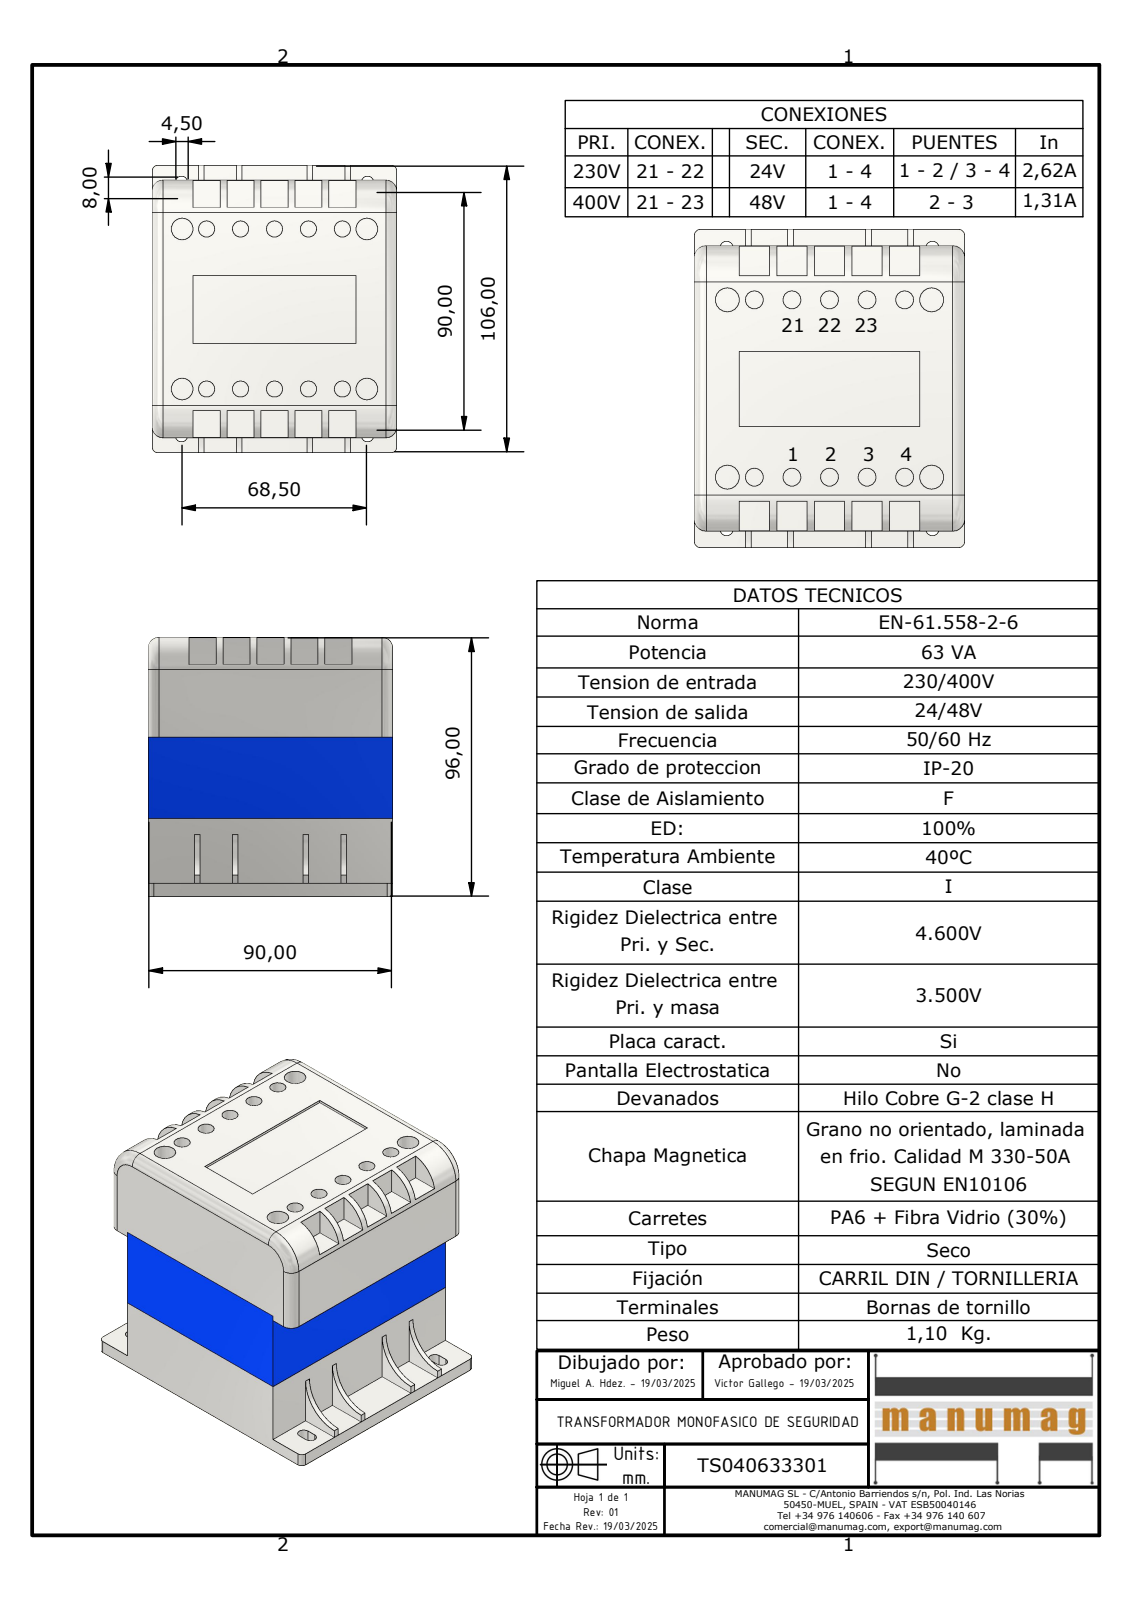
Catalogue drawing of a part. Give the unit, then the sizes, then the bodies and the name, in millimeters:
Units: millimetres
Overall size (bounding box): 106 × 96 × 90
Round holes (diameter × count): ⌀6 ×10, ⌀8 ×4
Partial cylindrical surfaces — rounded edges, fillets, slot ends (radius × count): R2.25 ×8, R4 ×6, R2 ×4, R12 ×2, R15 ×2
Main face-to-face distances: 1, 75, 90, 5, 89, 56, 61, 76, 74, 91
Hole centre spacings: 59, 12.5, 60.31, 25, 64.08, 9, 21.5, 34
Volume: 349 677 mm³ · Surface area: 95 183 mm²
Bodies: 11 solids, 188 faces (142 planar, 42 cylindrical, 4 other)
Part name (STEP PRODUCT): TS040633301; CENTRAL EI84-30; SUPERIOR EI84; INFERIOR EI84
STEP written by: Autodesk Inventor 2023 (AUTOMOTIVE_DESIGN)
